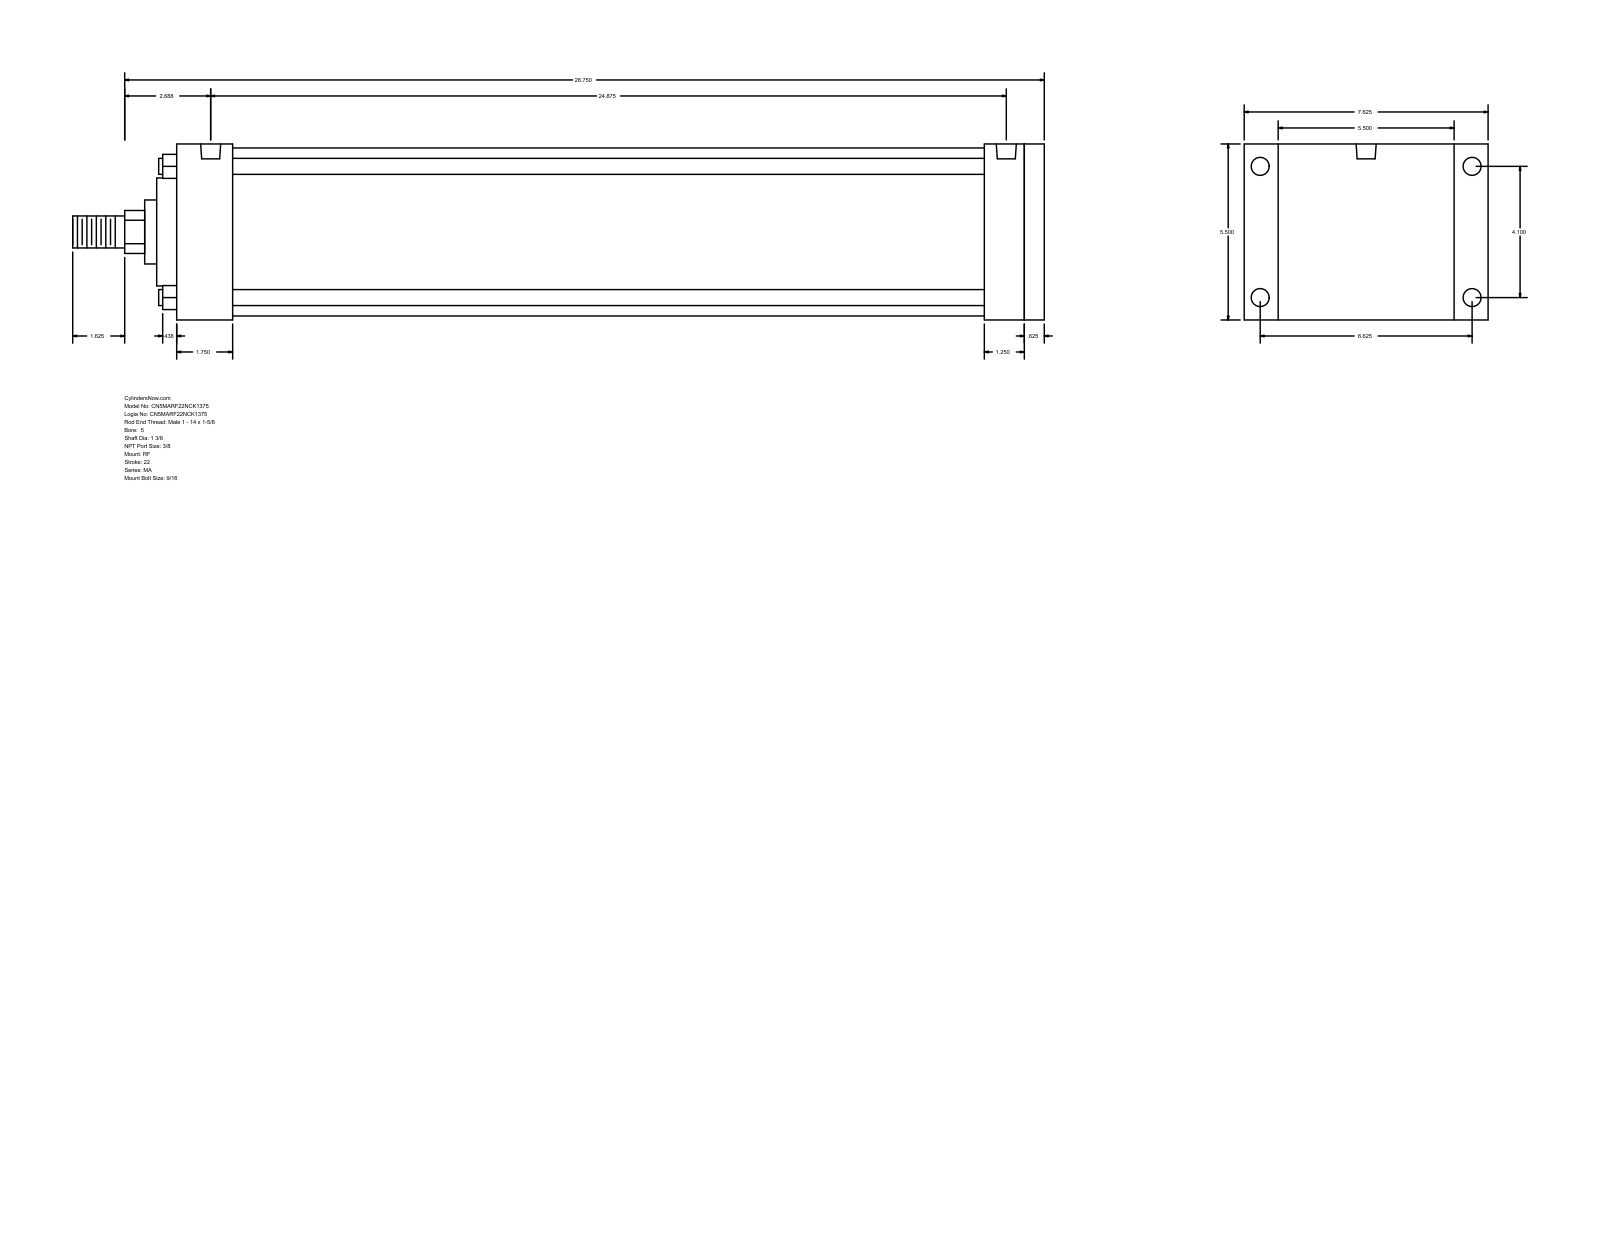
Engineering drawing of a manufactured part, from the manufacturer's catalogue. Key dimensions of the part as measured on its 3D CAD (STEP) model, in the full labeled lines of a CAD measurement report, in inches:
Part name (STEP PRODUCT): MA_RF__0500_1.375
STEP written by: GSSL Pune (CONFIG_CONTROL_DESIGN)
Units: inches
Bodies: 0 solids, 94 faces (65 planar, 29 cylindrical, 0 other)
Overall size (bounding box): 30.375 × 7.625 × 5.5
Round holes (diameter × count): ⌀0.437 ×4, ⌀0.563 ×4, ⌀0.627 ×2
Round bosses / shafts (diameter × count): ⌀0.5 ×4, ⌀5.25 ×1, ⌀3.375 ×1, ⌀2 ×1, ⌀1.375 ×1, ⌀1 ×1
Partial cylindrical surfaces — rounded edges, fillets, slot ends (radius × count): R0.672 ×1
Main face-to-face distances: 5.5, 27.125, 0.625, 26.5, 1.75, 24.75, 25.375, 25.25, 23.5, 1.25
Hole centre spacings: 4.1, 6.625, 7.791, 24.5, 0.187, 0.188, 24.687, 24.688
